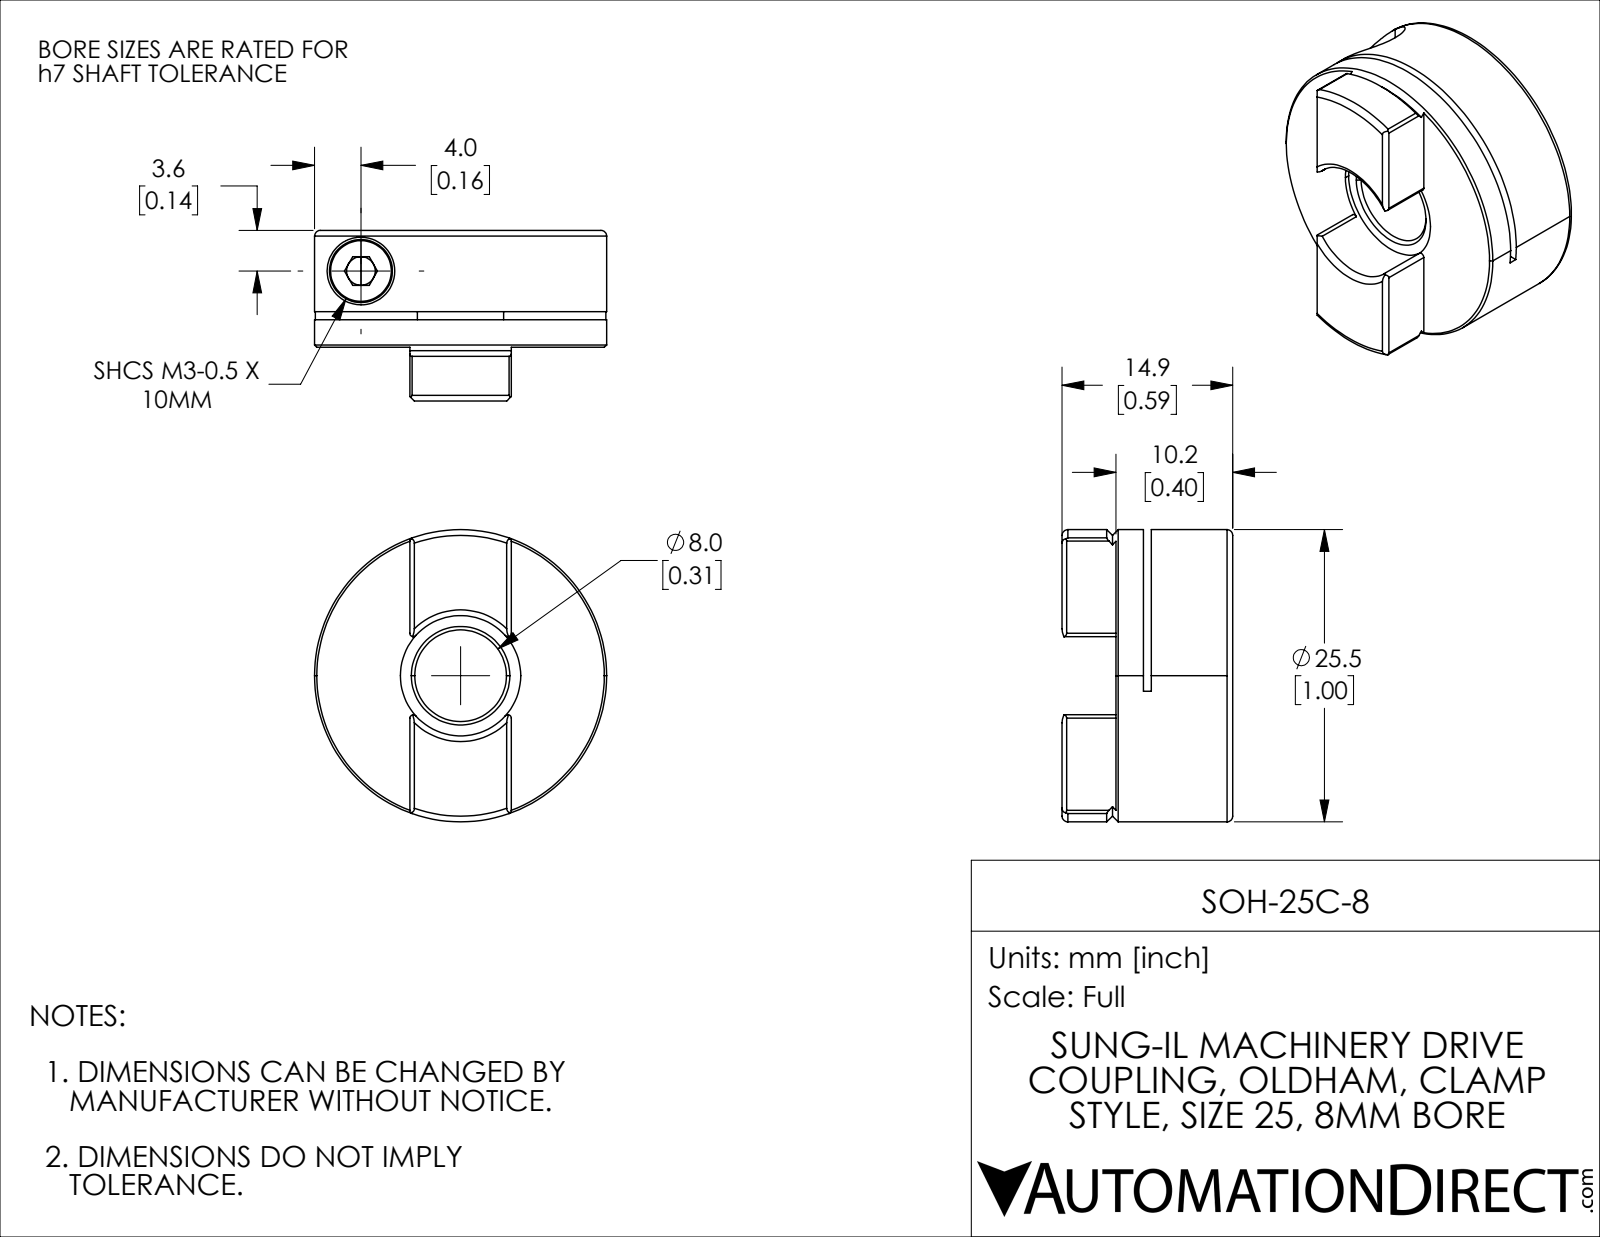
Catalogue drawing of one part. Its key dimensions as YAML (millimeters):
part_name: "SOH-25C-8"
step_written_by: "SolidWorks 2021 (CONFIG_CONTROL_DESIGN)"
units: millimeters
bodies: {solids: 2, faces: 97, planar: 39, cylindrical: 33, other: 25}
overall_size: [25.5, 25.5, 14.9]
volume: 4974
surface_area: 3278
round_holes:
  - {diameter: 2.5, count: 1}
  - {diameter: 3.3, count: 1}
  - {diameter: 5.9, count: 1}
  - {diameter: 8, count: 1}
  - {diameter: 10.5, count: 1}
round_bosses_or_shafts:
  - {diameter: 25.5, count: 1}
  - {diameter: 5.5, count: 1}
  - {diameter: 3, count: 1}
partial_cylinders:
  - {radius: 0.3, count: 8}
  - {radius: 22.5, count: 1}
face_to_face_distances: [7.8, 7.1, 10.2, 2.4, 0.7, 3.1, 14.9, 4.7, 0.8, 8.86]
